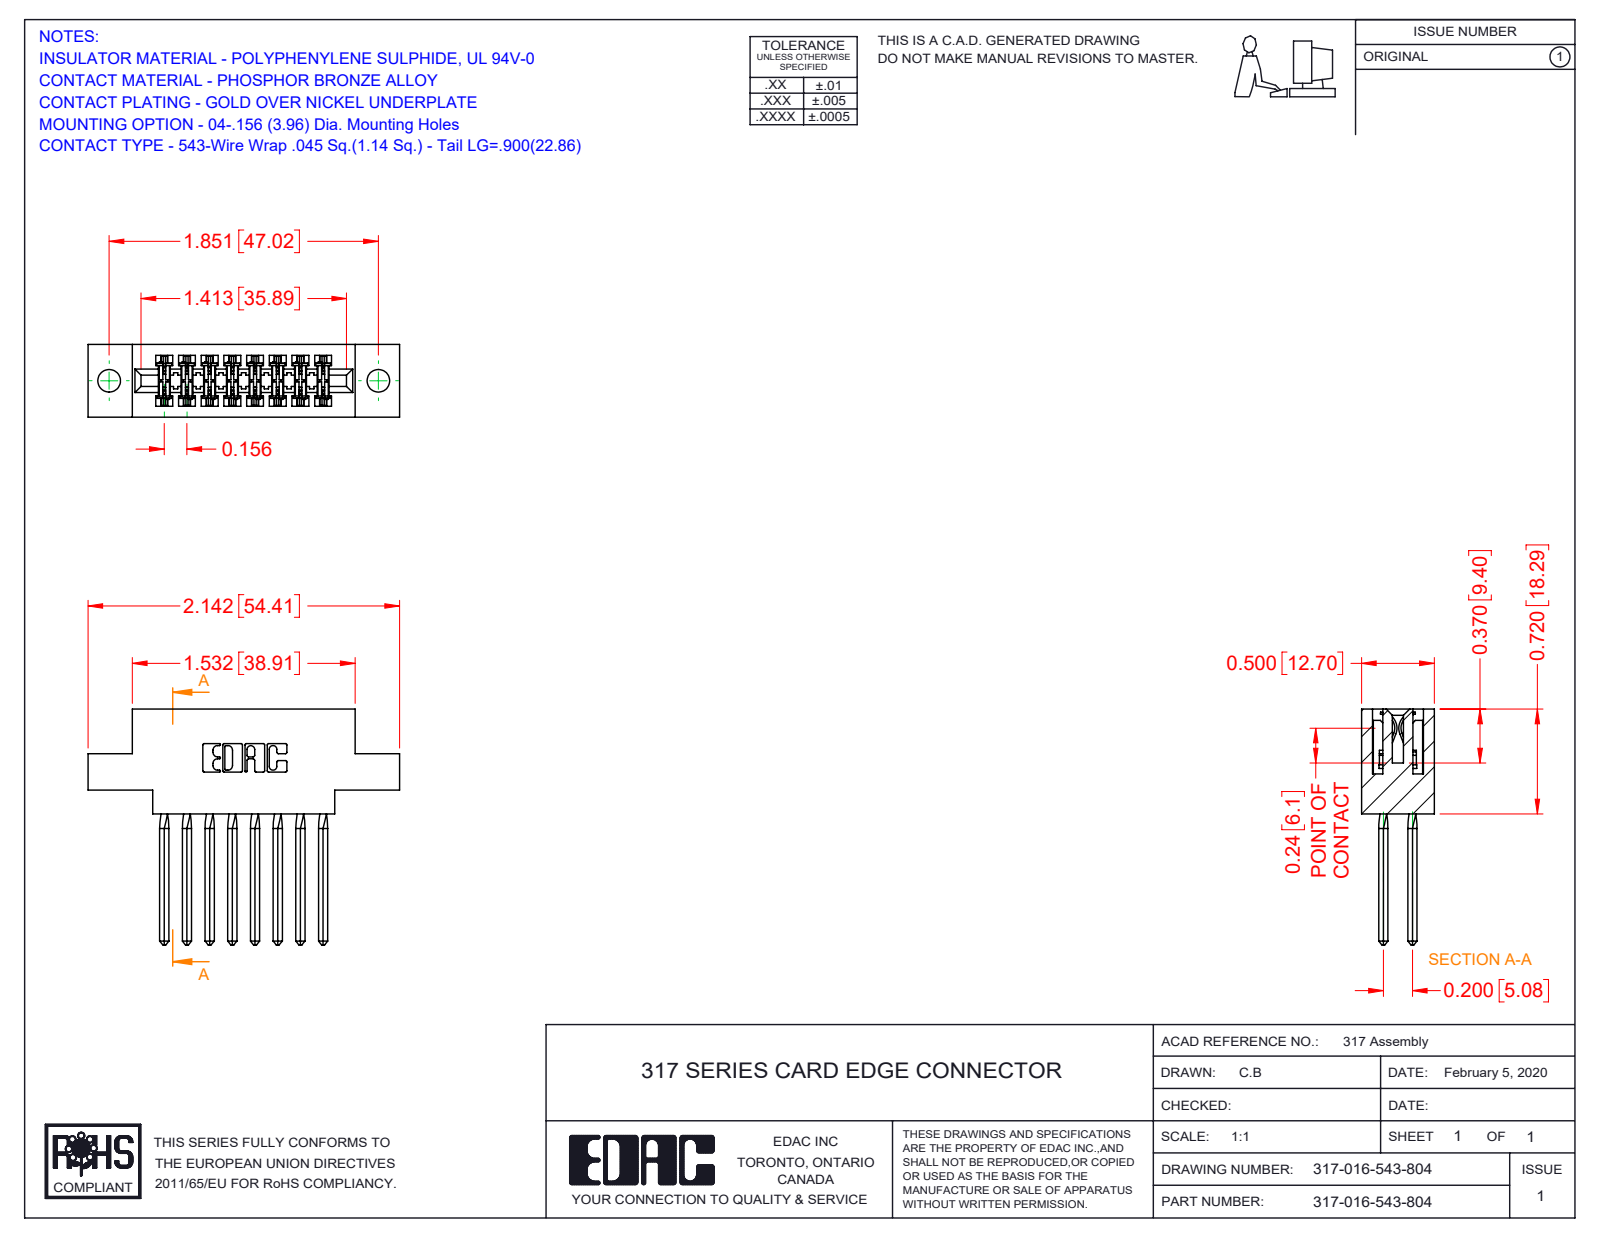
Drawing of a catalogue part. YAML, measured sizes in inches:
part_name: "317 Part_.156 Dia - TH; 317-290-001_543; 317-016-543-804"
step_written_by: "SolidWorks 2016 (CONFIG_CONTROL_DESIGN)"
units: inches
bodies: {solids: 17, faces: 1526, planar: 1226, cylindrical: 236, other: 64}
overall_size: [2.142, 1.62, 0.5]
volume: 0.487
surface_area: 16.41
round_holes:
  - {diameter: 0.156, count: 2}
partial_cylinders:
  - {radius: 0.015, count: 32}
  - {radius: 0.01, count: 22}
  - {radius: 0.007, count: 6}
  - {radius: 0.031, count: 6}
  - {radius: 0.026, count: 3}
  - {radius: 0.095, count: 2}
  - {radius: 0.1, count: 2}
  - {radius: 0.11, count: 2}
face_to_face_distances: [0.5, 0.11, 0.075, 0.425, 0.22, 0.156, 0.331, 0.116, 0.35, 0.163]
hole_center_spacings: [1.851]
